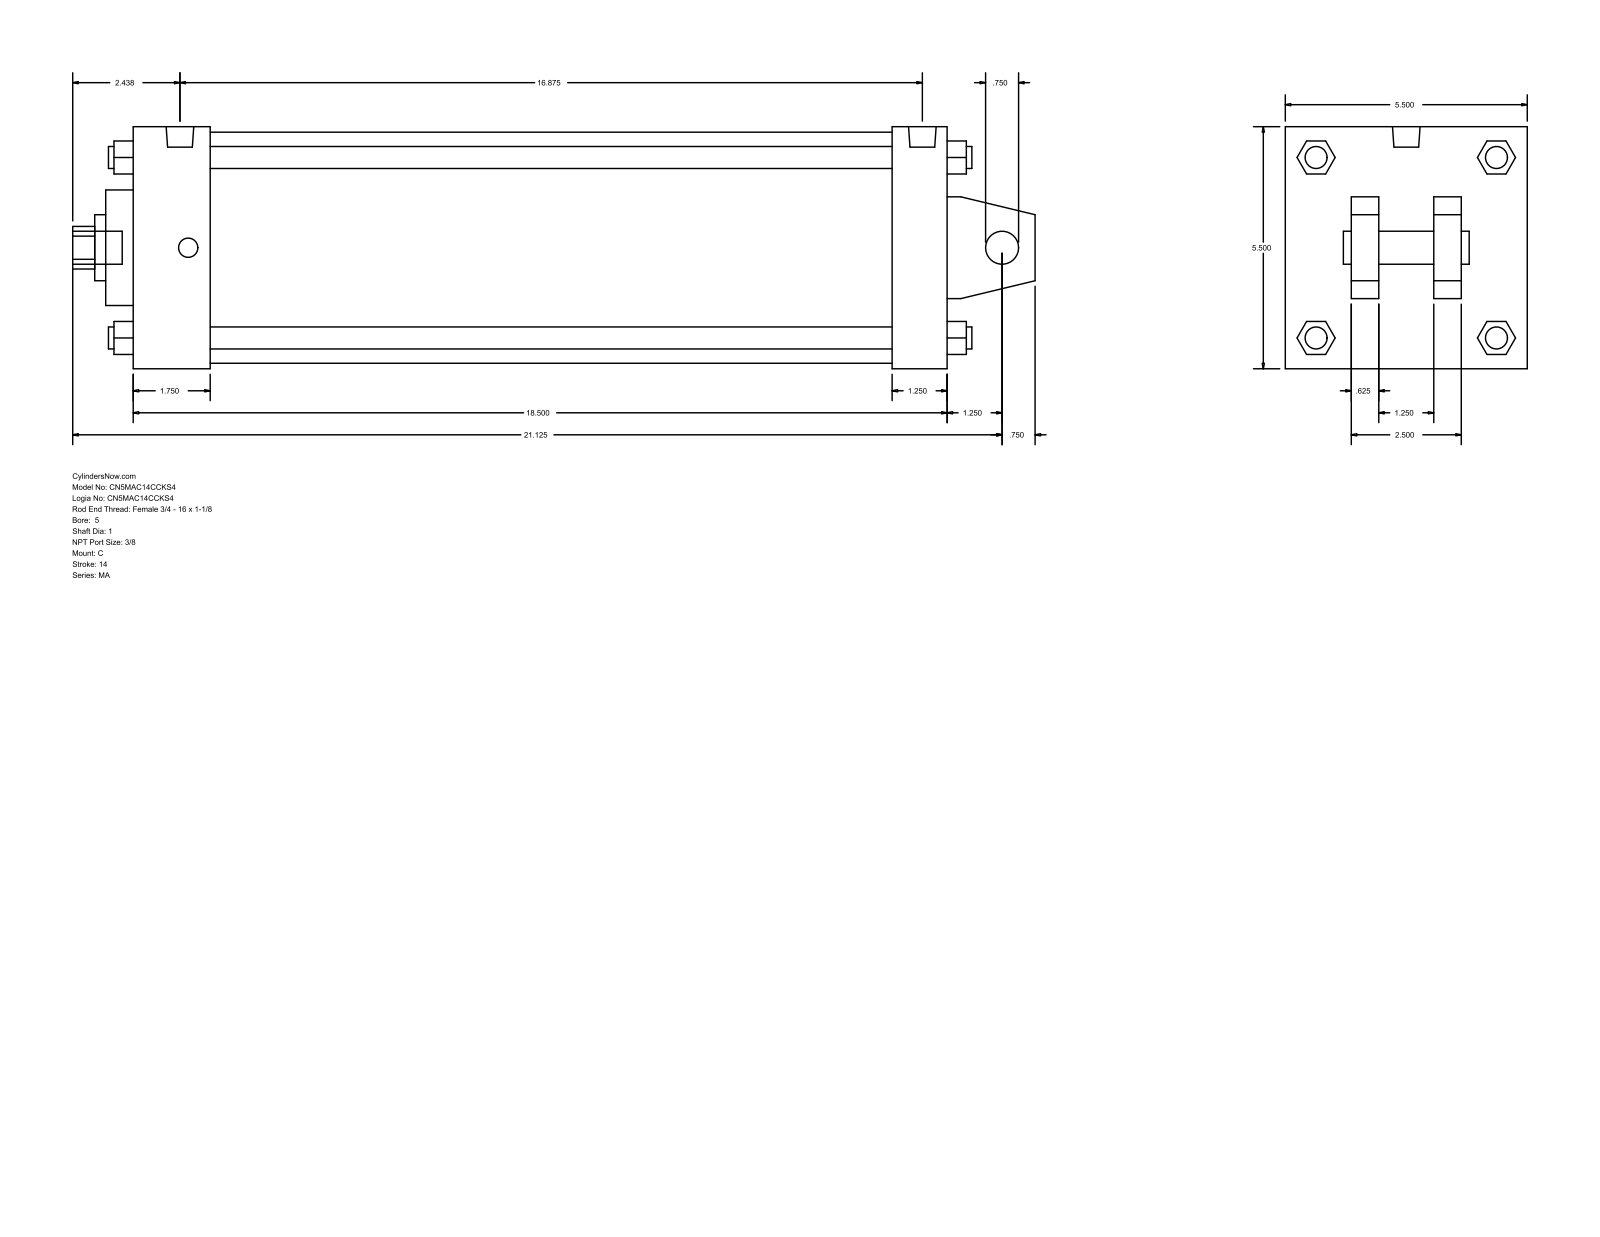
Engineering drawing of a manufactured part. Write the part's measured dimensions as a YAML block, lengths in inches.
part_name: "MA_C__0500_1"
step_written_by: "GSSL Pune (CONFIG_CONTROL_DESIGN)"
units: inches
bodies: {solids: 0, faces: 141, planar: 109, cylindrical: 32, other: 0}
overall_size: [21.875, 5.5, 5.5]
round_holes:
  - {diameter: 0.75, count: 1}
  - {diameter: 1, count: 1}
  - {diameter: 1.5, count: 1}
  - {diameter: 2.625, count: 1}
  - {diameter: 5.25, count: 1}
round_bosses_or_shafts:
  - {diameter: 0.5, count: 4}
  - {diameter: 0.437, count: 4}
  - {diameter: 0.627, count: 2}
  - {diameter: 0.75, count: 1}
partial_cylinders:
  - {radius: 0.484, count: 1}
face_to_face_distances: [5.5, 18.5, 0.625, 17.25, 1.25, 1.75, 15.5, 16.75, 1.5, 4]
